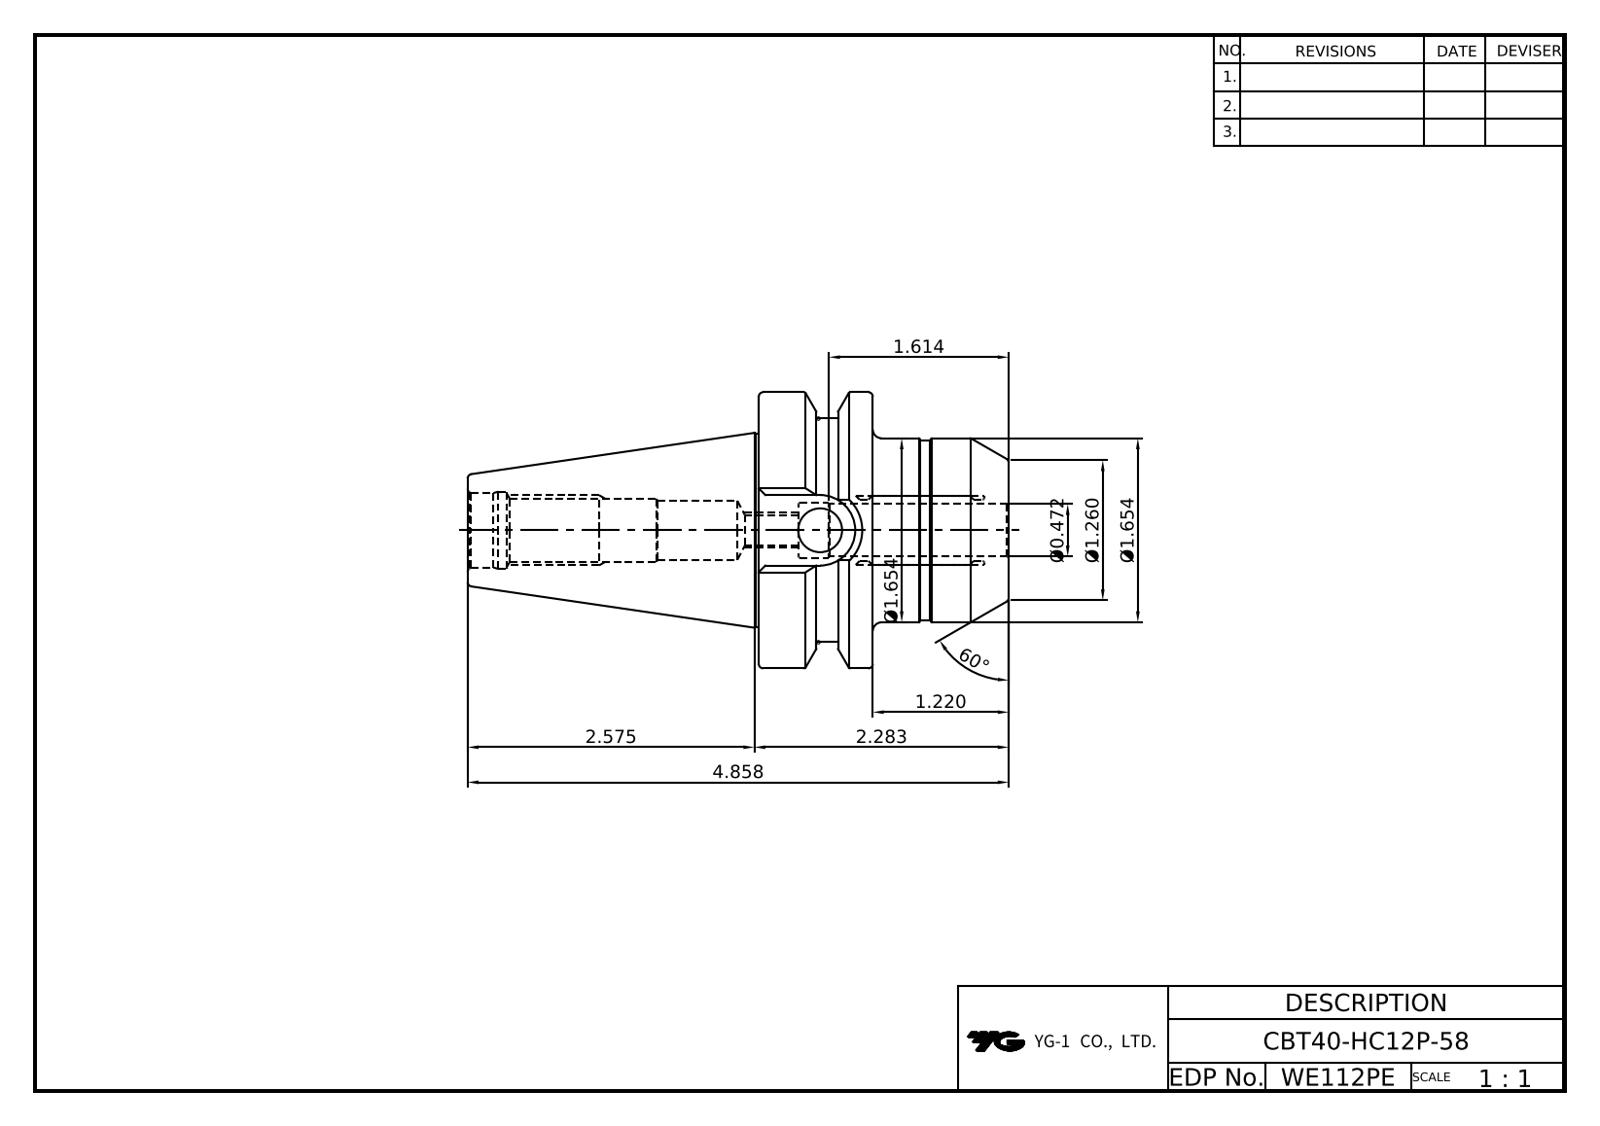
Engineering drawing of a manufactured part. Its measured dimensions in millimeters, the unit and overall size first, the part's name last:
Units: millimetres
Overall size (bounding box): 123.4 × 63 × 63
Round holes (diameter × count): ⌀6.92 ×1, ⌀12 ×1, ⌀12.8 ×1, ⌀13.5 ×1, ⌀13.84 ×1, ⌀17 ×1, ⌀17.6 ×1
Round bosses / shafts (diameter × count): ⌀63 ×1, ⌀51 ×1, ⌀44 ×1, ⌀42 ×1, ⌀41 ×1
Partial cylindrical surfaces — rounded edges, fillets, slot ends (radius × count): R8.05 ×1
Main face-to-face distances: 26, 57, 31, 45.2, 66.4, 18.1, 7.9, 38.9, 13.1, 5
Volume: 158 899 mm³ · Surface area: 27 127 mm²
Bodies: 1 solid, 72 faces (24 planar, 18 cylindrical, 30 other)
Part name (STEP PRODUCT): LO-CBT40-HC12P-58
STEP written by: Autodesk Inventor 2022 (AUTOMOTIVE_DESIGN)
